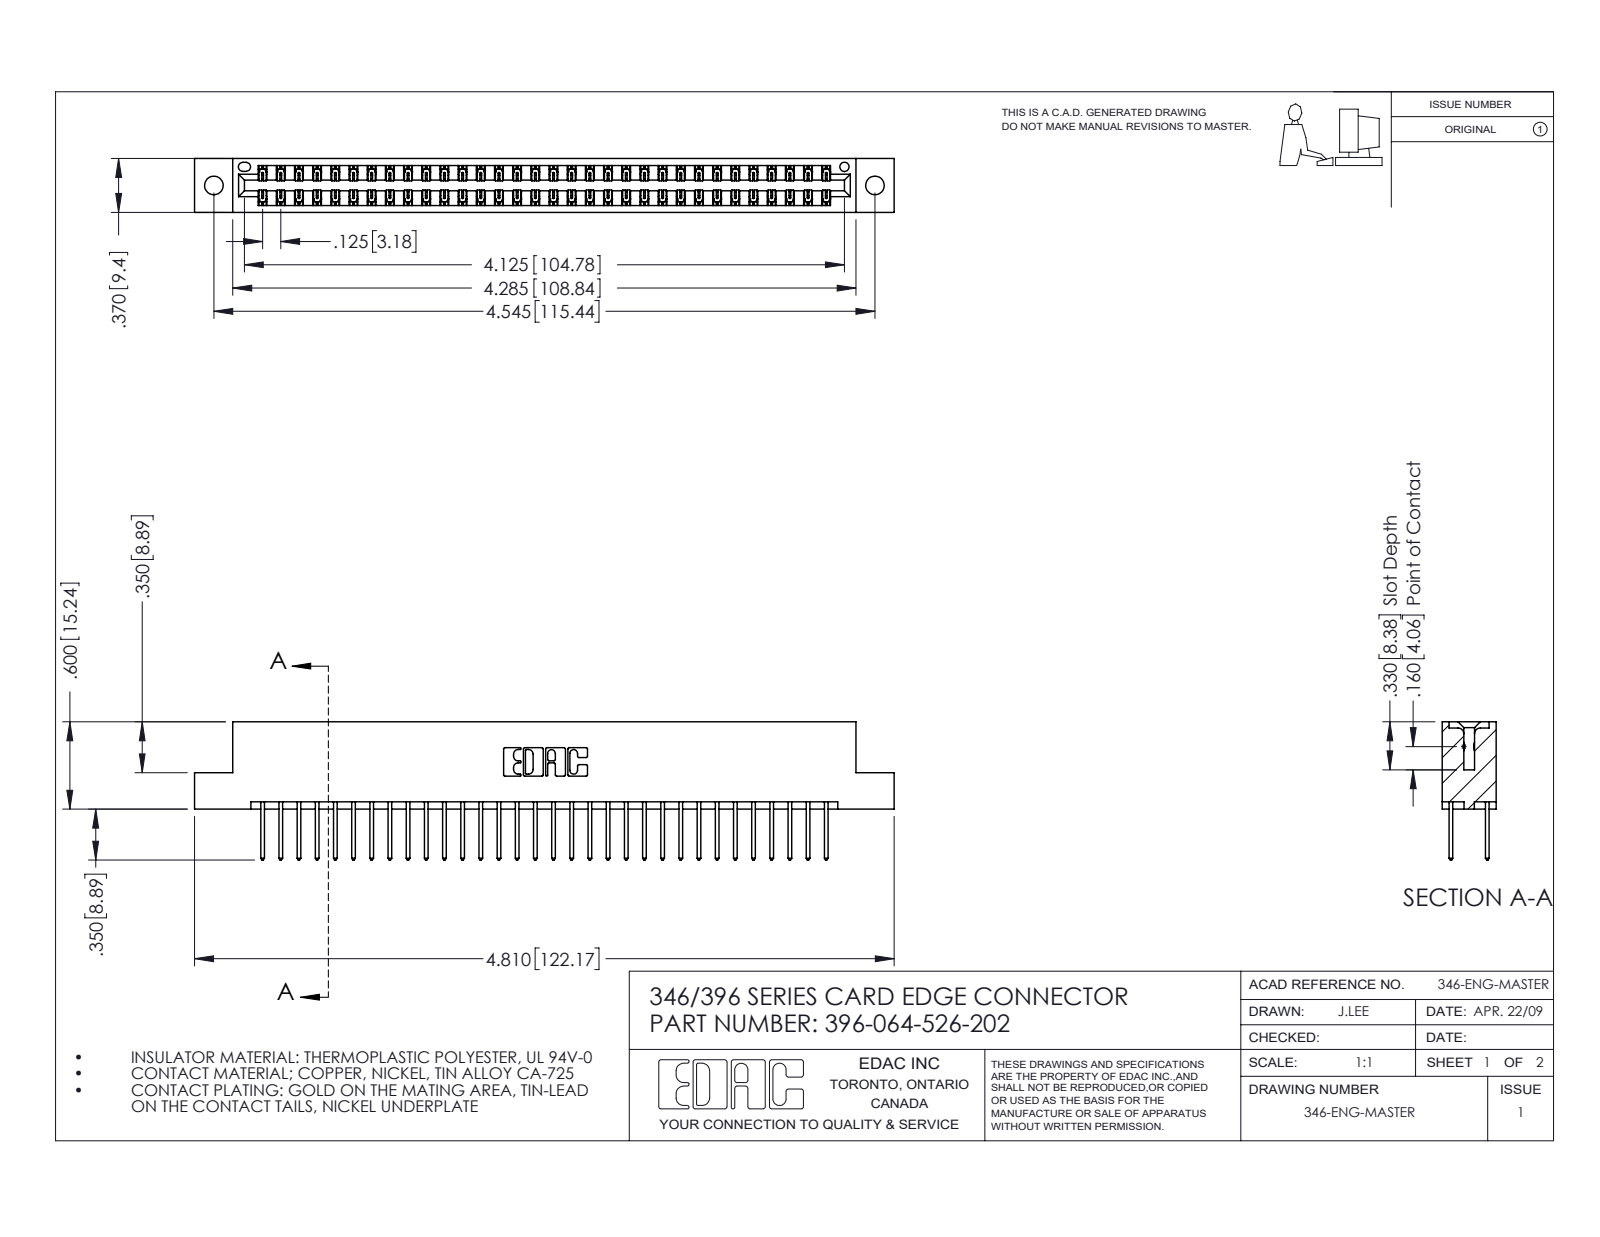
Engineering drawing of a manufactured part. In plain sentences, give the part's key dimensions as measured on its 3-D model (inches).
The part is named "396-064-526-202; 345-292-001_345-293-126; 346 Part_Flush Mounting Lugs - 0.128 Dia". Its 3-D file was written by "SolidWorks 2016 (CONFIG_CONTROL_DESIGN)". It is 65 solids with 3450 faces: 2316 planar, 1134 cylindrical and 0 other. Overall it measures 4.81 by 0.95 by 0.37 inches. Its volume is 0.726 cubic inches and its surface area 25.43 square inches. Round holes: 2 of diameter 0.128, 1 of diameter 0.064. Partial cylindrical surfaces (rounded edges, fillets, slot ends): 96 of radius 0.006, 64 of radius 0.01, 22 of radius 0.01, 6 of radius 0.007, 6 of radius 0.031, 3 of radius 0.026, 2 of radius 0.014, 2 of radius 0.022. The main face-to-face distances are 0.048, 0.322, 0.25, 0.37, 0.072, 0.298, 0.025, 0.275, 0.148, 0.222. The hole center spacings are 0.246, 4.337, 4.545.
